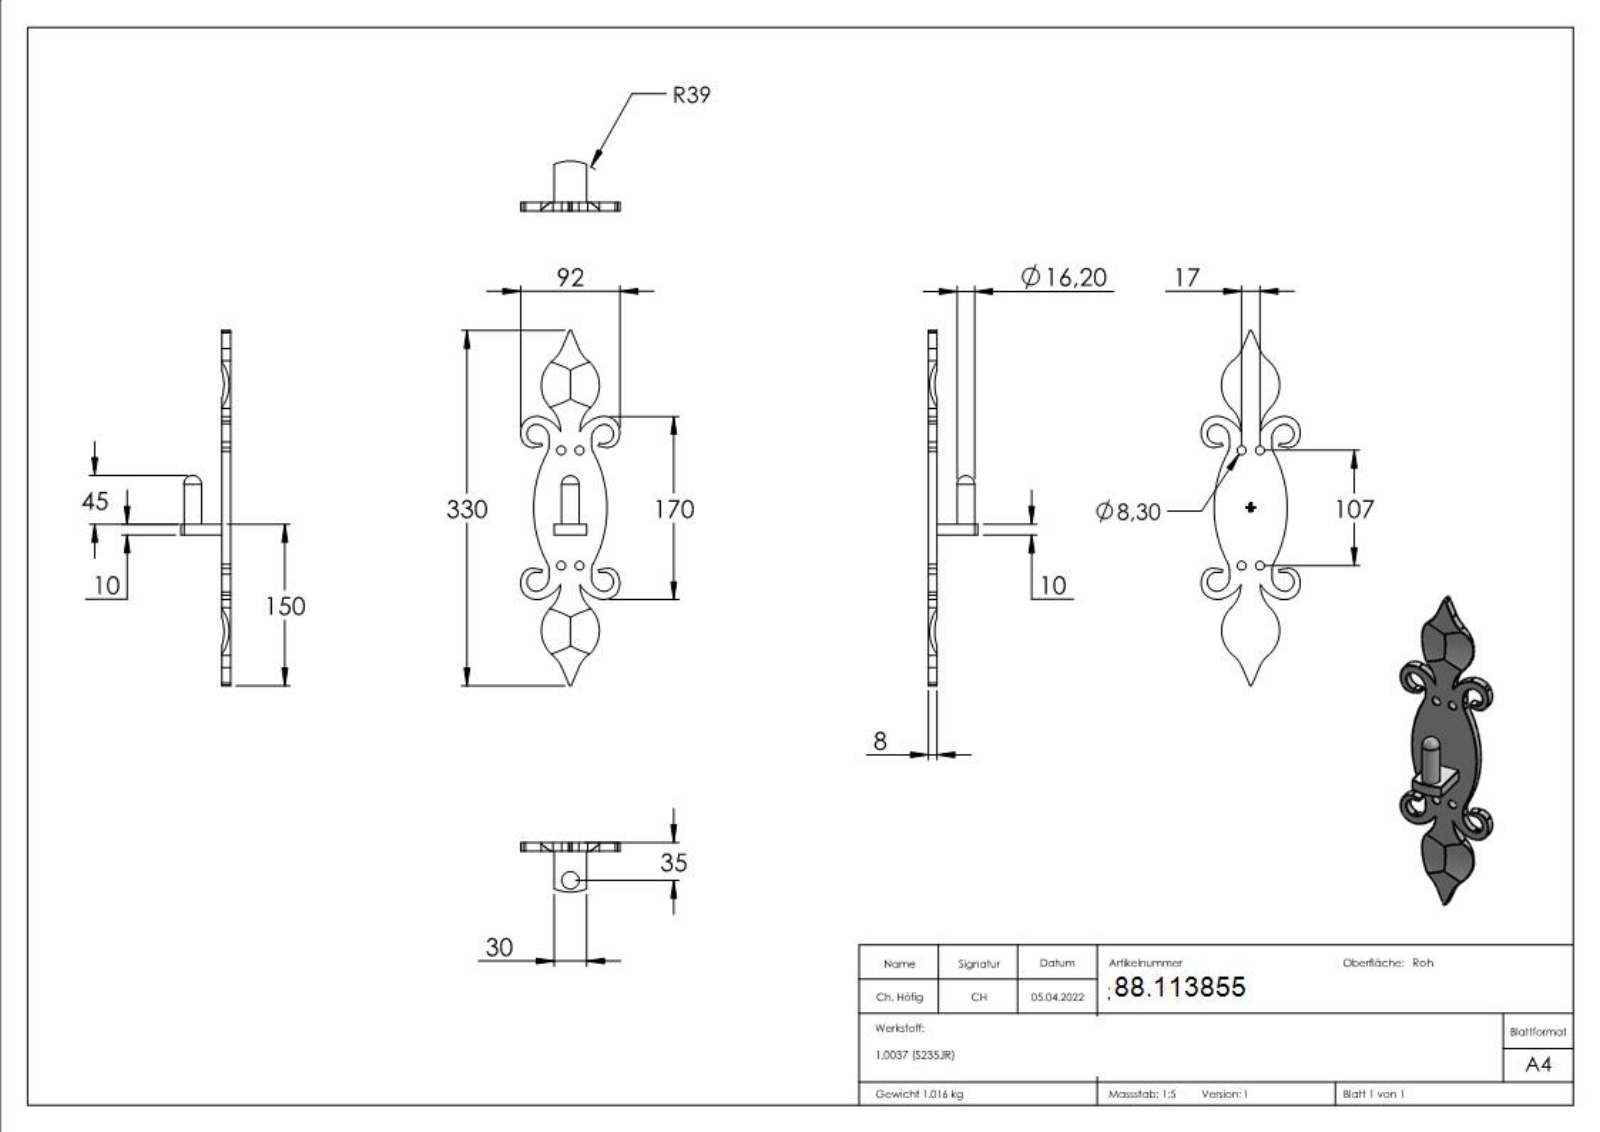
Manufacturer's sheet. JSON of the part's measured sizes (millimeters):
{"part_name": "3855", "step_written_by": "SolidWorks 2018 (CONFIG_CONTROL_DESIGN)", "units": "millimeters", "bodies": {"solids": 1, "faces": 319, "planar": 129, "cylindrical": 70, "other": 120}, "overall_size": [330, 92, 46], "volume_mm3": 130197, "surface_area_mm2": 45461, "round_holes": [[8.3, 4]], "round_bosses_or_shafts": [[16.2, 1]], "partial_cylinders_radius": [[30, 20], [10, 12], [16, 8], [39, 5], [7, 4], [9, 4], [13, 4], [18, 4]], "face_to_face_distances": [8, 10, 30, 132.7, 4.75, 34.75, 39.5, 16.66, 7.9, 0.34], "hole_center_spacings": [17, 107, 108.34]}
